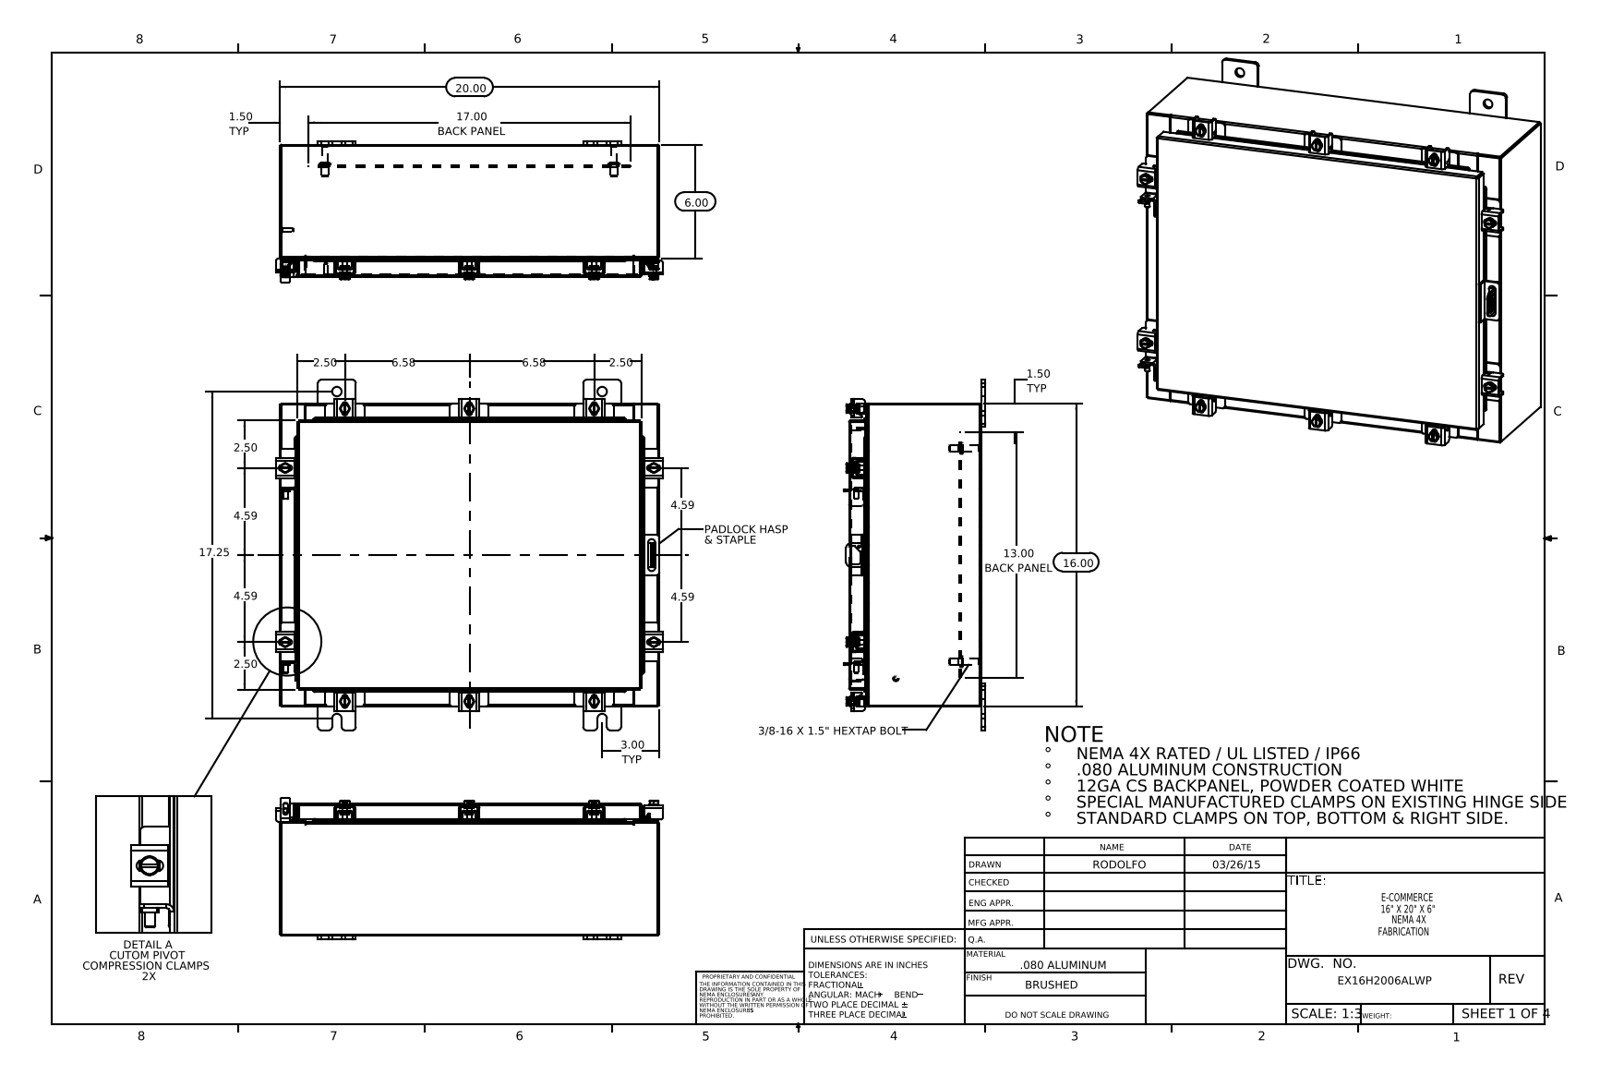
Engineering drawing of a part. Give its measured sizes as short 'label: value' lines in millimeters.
name: N-WMT04X30402202210-00 22104005_DEFAULT; EX16H2006ALWP Clamp Assembly; EX16H2006ALWP Bottom; EX16H2006ALWP Padlock Staple (+8 more)
written by: SolidWorks 2014 (AUTOMOTIVE_DESIGN)
unit: mm
bodies: 71 solids, 1768 faces (943 planar, 681 cylindrical, 144 other)
size: 518.7 × 469.9 × 189.3
volume: 2 009 000 mm³; area: 1 985 000 mm²
holes: 10× ⌀5.4, 10× ⌀6.6, 8× ⌀12.7, 1× ⌀3.2, 1× ⌀6.4
bosses: 10× ⌀12.7, 10× ⌀6.4, 8× ⌀10.1, 4× ⌀15.9, 4× ⌀9.5, 4× ⌀8.4, 2× ⌀8, 2× ⌀6
rounds: 44× R1.5, 24× R4.8, 22× R0.3, 22× R2.2, 20× R3.6, 18× R3, 16× R2.3, 16× R2.5
face distances: 1.9, 175.3, 177.2, 173.4, 404.5, 25.4, 27.3, 148, 149.9, 29.9
hole spacings: 59.6, 112.8, 265, 323, 340.2, 421.7, 519, 392.5
